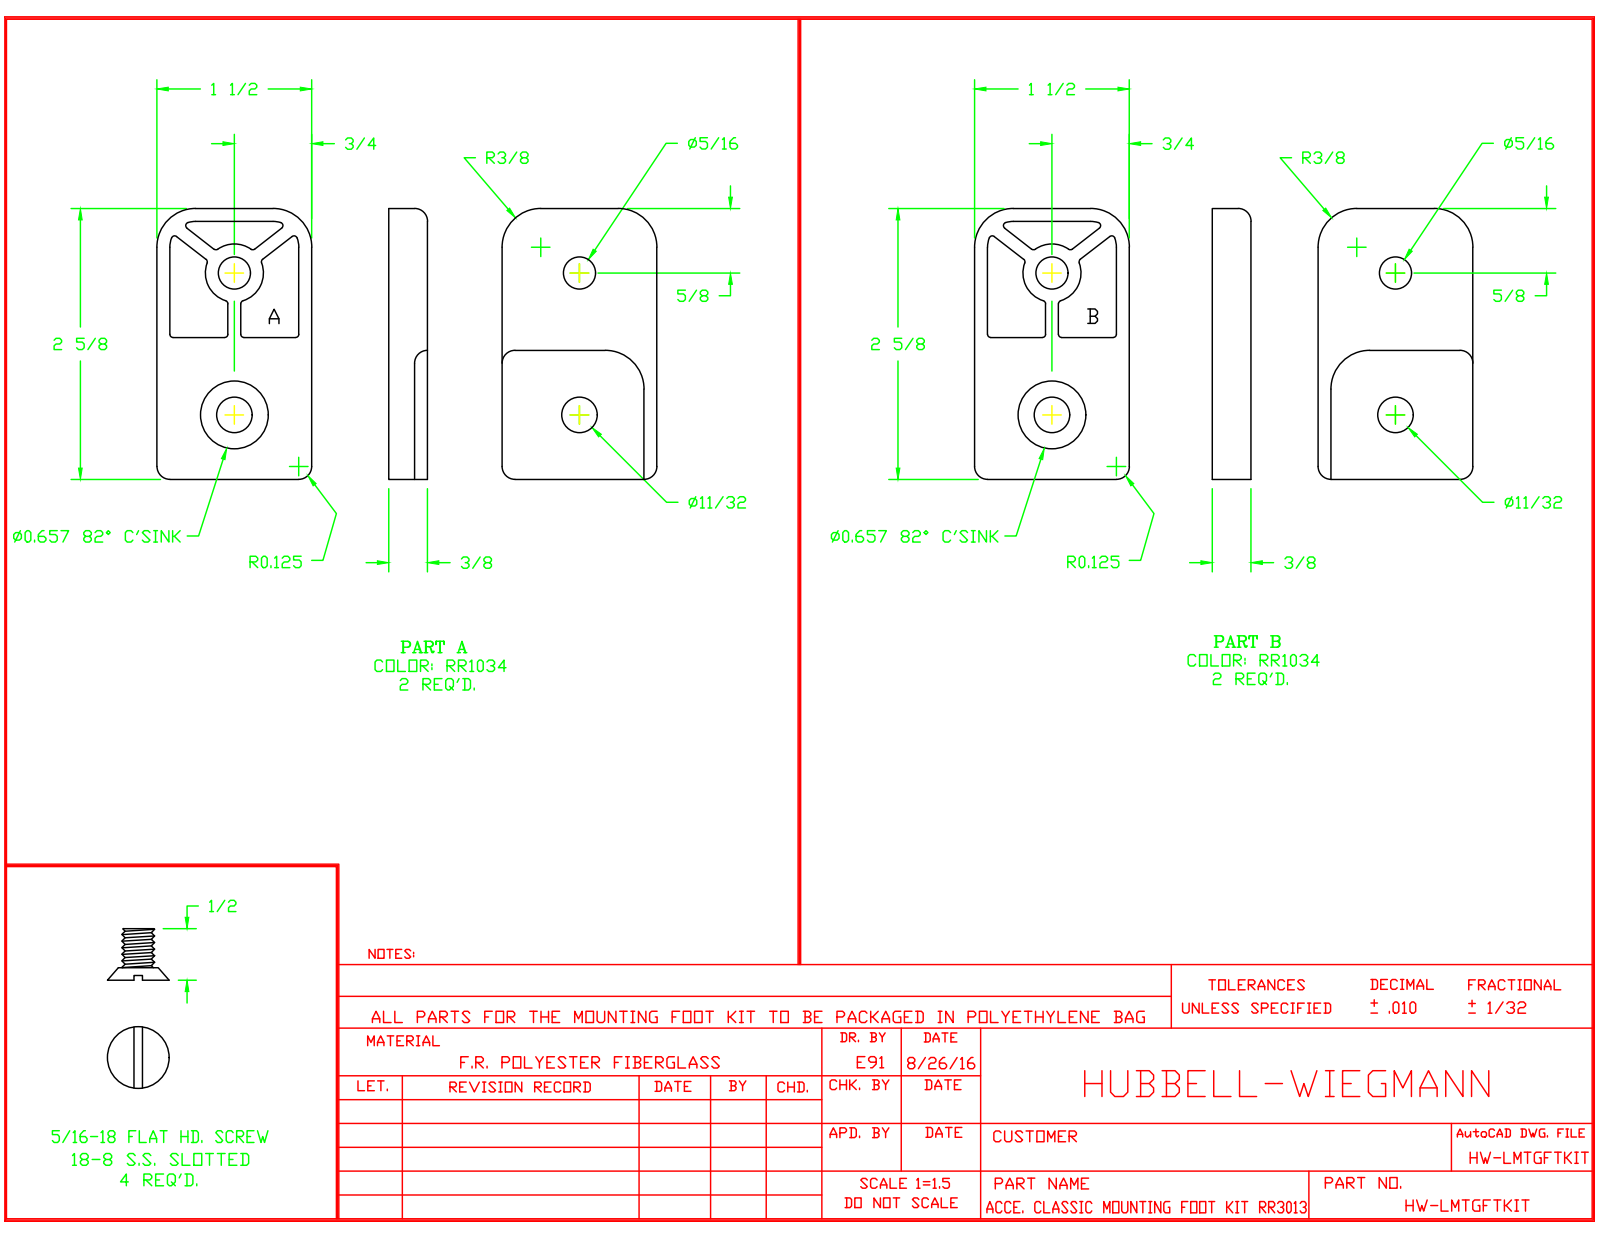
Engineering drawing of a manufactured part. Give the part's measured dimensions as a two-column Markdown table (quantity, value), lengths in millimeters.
| quantity | value |
| --- | --- |
| part name | CLMTGFTKIT_STP; CL MOUNTING SCREW; CLMTGFTKIT-B; CLMTGFTKIT-A |
| STEP written by | Autodesk Inventor 2017 (AUTOMOTIVE_DESIGN) |
| units | millimeters |
| bodies | 8 solids, 368 faces (172 planar, 120 cylindrical, 76 other) |
| overall size | 158.42 × 125.38 × 14.17 |
| volume | 72 880 mm³ |
| surface area | 33 188 mm² |
| round holes (diameter × count) | 7.95 × 4, 8.74 × 4 |
| round bosses / shafts (diameter × count) | 7.94 × 4 |
| partial cylindrical surfaces (radius × count) | 0.79 × 56, 2.54 × 12, 6.35 × 8, 3.17 × 4, 7.15 × 4, 9.53 × 2 |
| main face-to-face distances | 3.17, 6.35, 9.52, 3.18, 86.53, 1.47, 8.05, 4.88, 1.7, 90.87 |
| hole center spacings | 34.92, 34.93, 55.24, 85.95, 86.62, 90.16, 90.17, 93.08 |
